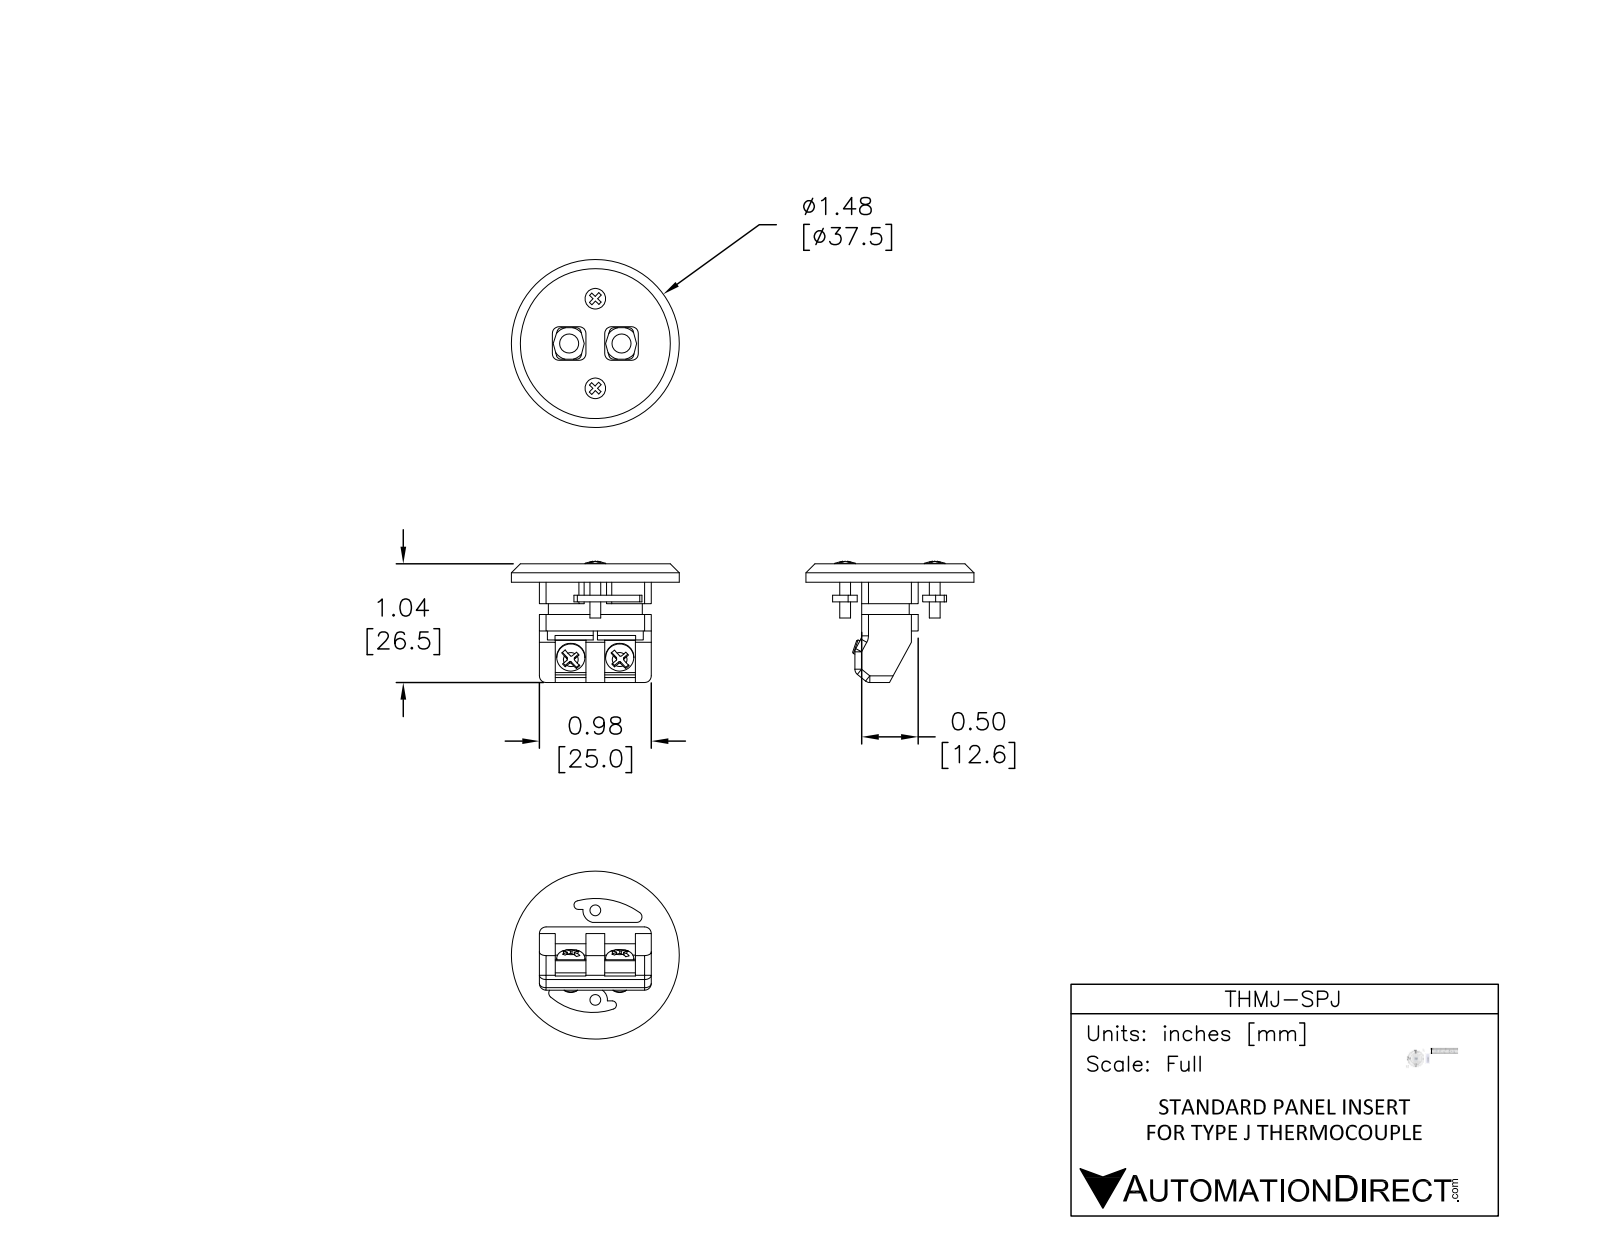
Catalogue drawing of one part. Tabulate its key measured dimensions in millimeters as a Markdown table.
| quantity | value |
| --- | --- |
| part name | THMJ-SPJ |
| STEP written by | SolidWorks 2017 (AUTOMOTIVE_DESIGN) |
| units | millimeters |
| bodies | 1 solid, 310 faces (201 planar, 85 cylindrical, 24 other) |
| overall size | 37.5 × 37.5 × 27.06 |
| volume | 9 567 mm³ |
| surface area | 5 667 mm² |
| round holes (diameter × count) | 4.25 × 2 |
| round bosses / shafts (diameter × count) | 6.3 × 2, 4.6 × 2, 3.2 × 2, 2.4 × 2, 37.5 × 1 |
| partial cylindrical surfaces (radius × count) | 1.5 × 24, 0.25 × 8, 1 × 8, 0.92 × 1, 0.98 × 1, 1.16 × 1, 1.22 × 1, 2.7 × 1 |
| main face-to-face distances | 4.1, 2, 12.6, 25, 1.5, 7, 10.9, 15, 8.5, 1 |
| hole center spacings | 11.7 |
